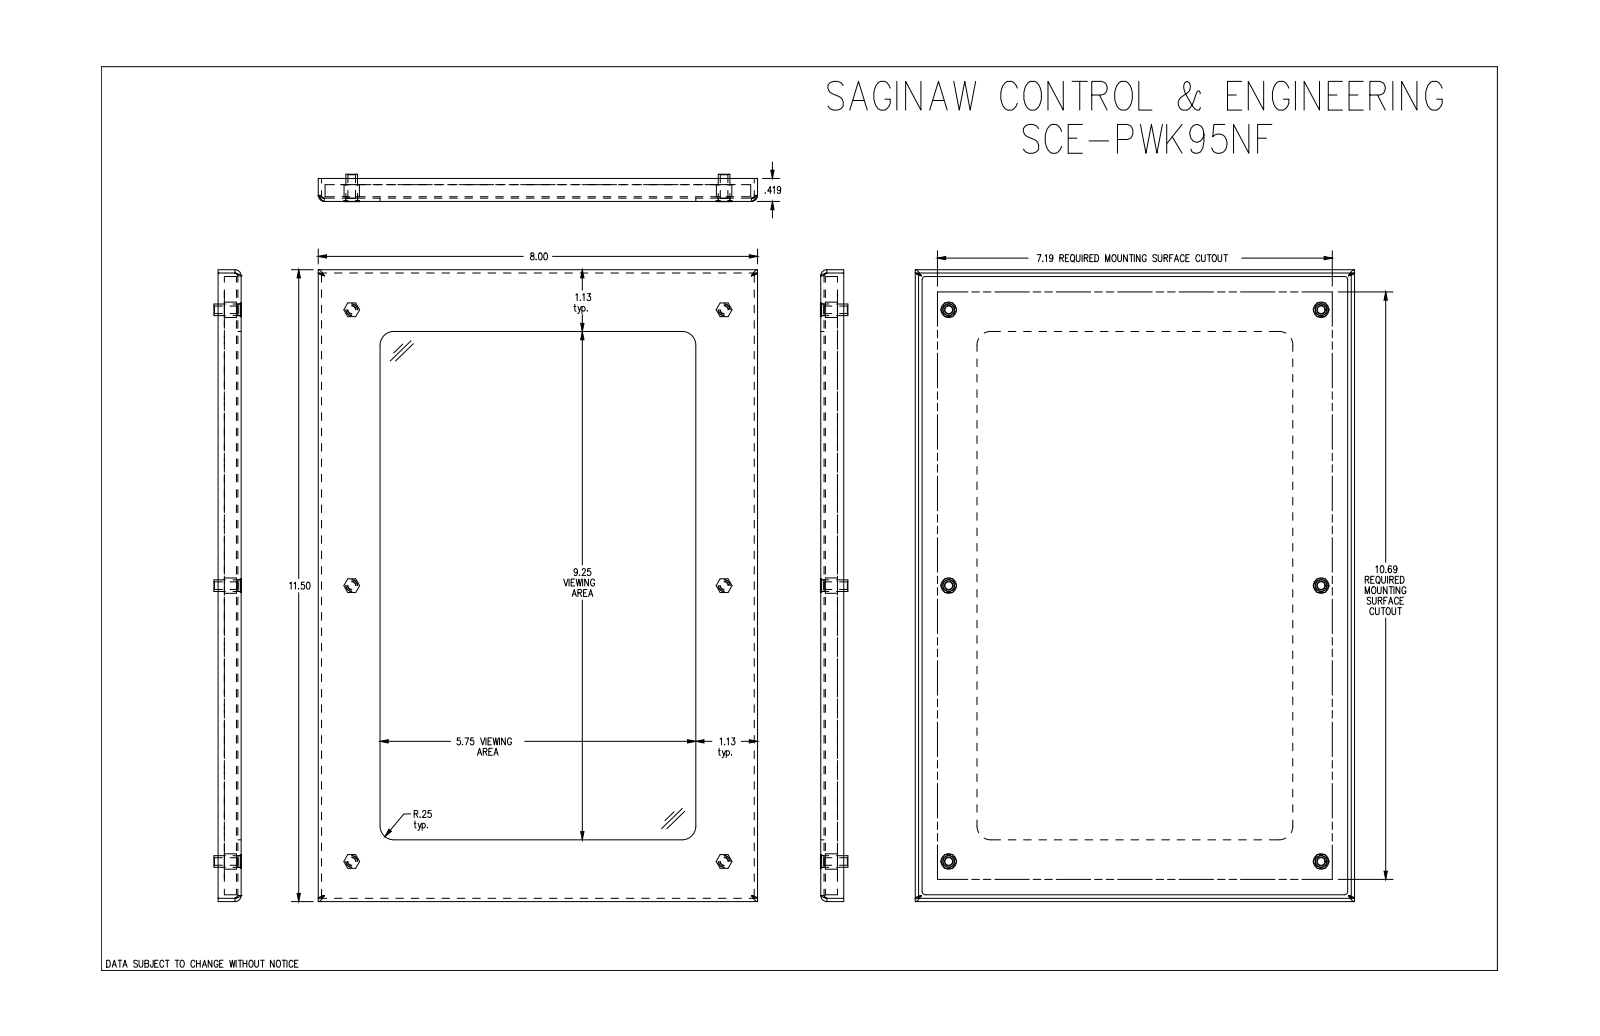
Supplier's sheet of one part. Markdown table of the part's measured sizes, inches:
| quantity | value |
| --- | --- |
| part name | SCE-PWK95NF |
| STEP written by | SolidWorks 2021 (AUTOMOTIVE_DESIGN) |
| units | inches |
| bodies | 8 solids, 147 faces (81 planar, 54 cylindrical, 12 other) |
| overall size | 11.5 × 8 × 0.5 |
| volume | 23.61 in³ |
| surface area | 295.5 in² |
| round holes (diameter × count) | 0.138 × 6, 0.213 × 6, 0.28 × 6 |
| round bosses / shafts (diameter × count) | 0.212 × 6 |
| partial cylindrical surfaces (radius × count) | 0.06 × 4, 0.112 × 4, 0.25 × 4 |
| main face-to-face distances | 0.236, 0.06, 0.261, 0.025, 0.321, 0.085, 7.94, 0.125, 7.875, 0.065 |
| hole center spacings | 5.02, 8.437, 6.781, 10.039, 12.115 |
